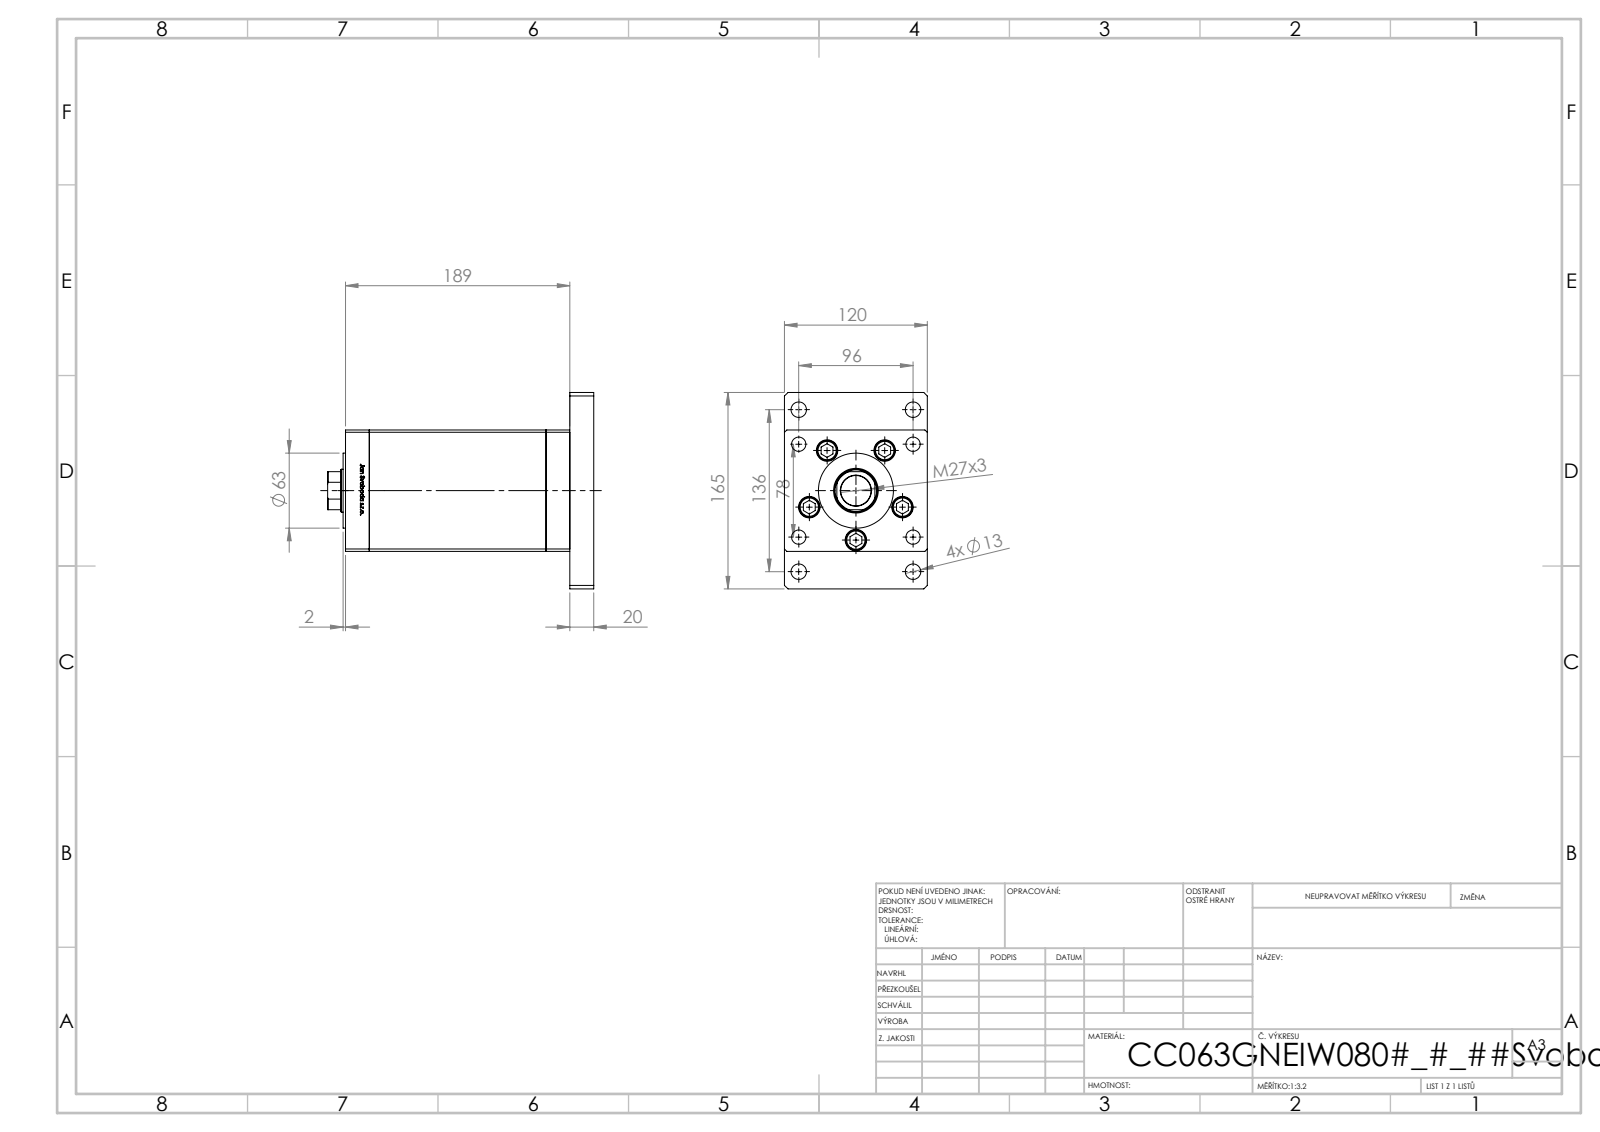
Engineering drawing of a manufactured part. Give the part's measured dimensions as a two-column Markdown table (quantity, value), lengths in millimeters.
| quantity | value |
| --- | --- |
| part name | V220C BACK_G; V220C_G_MIDDLE; ALLEN BOLT; V220C_VC_G (+2 more) |
| STEP written by | SolidWorks 2019 (CONFIG_CONTROL_DESIGN) |
| units | millimeters |
| bodies | 19 solids, 1313 faces (518 planar, 189 cylindrical, 606 other) |
| overall size | 223.5 × 165 × 120 |
| volume | 2 394 000 mm³ |
| surface area | 318 444 mm² |
| round holes (diameter × count) | 12 × 9, 13.5 × 5, 18 × 5, 13 × 4, 17 × 4, 2 × 2, 13.16 × 2, 25.5 × 1, 36 × 1, 37.5 × 1, 83 × 1 |
| round bosses / shafts (diameter × count) | 8 × 9, 17 × 5, 63 × 1 |
| partial cylindrical surfaces (radius × count) | 0.93 × 2, 17.5 × 1 |
| main face-to-face distances | 20, 168.5, 120, 188.5, 102, 148.5, 40, 2, 186.5, 18 |
| hole center spacings | 41.5, 29, 61.85, 83.23, 96, 100.28, 107, 143.75 |
